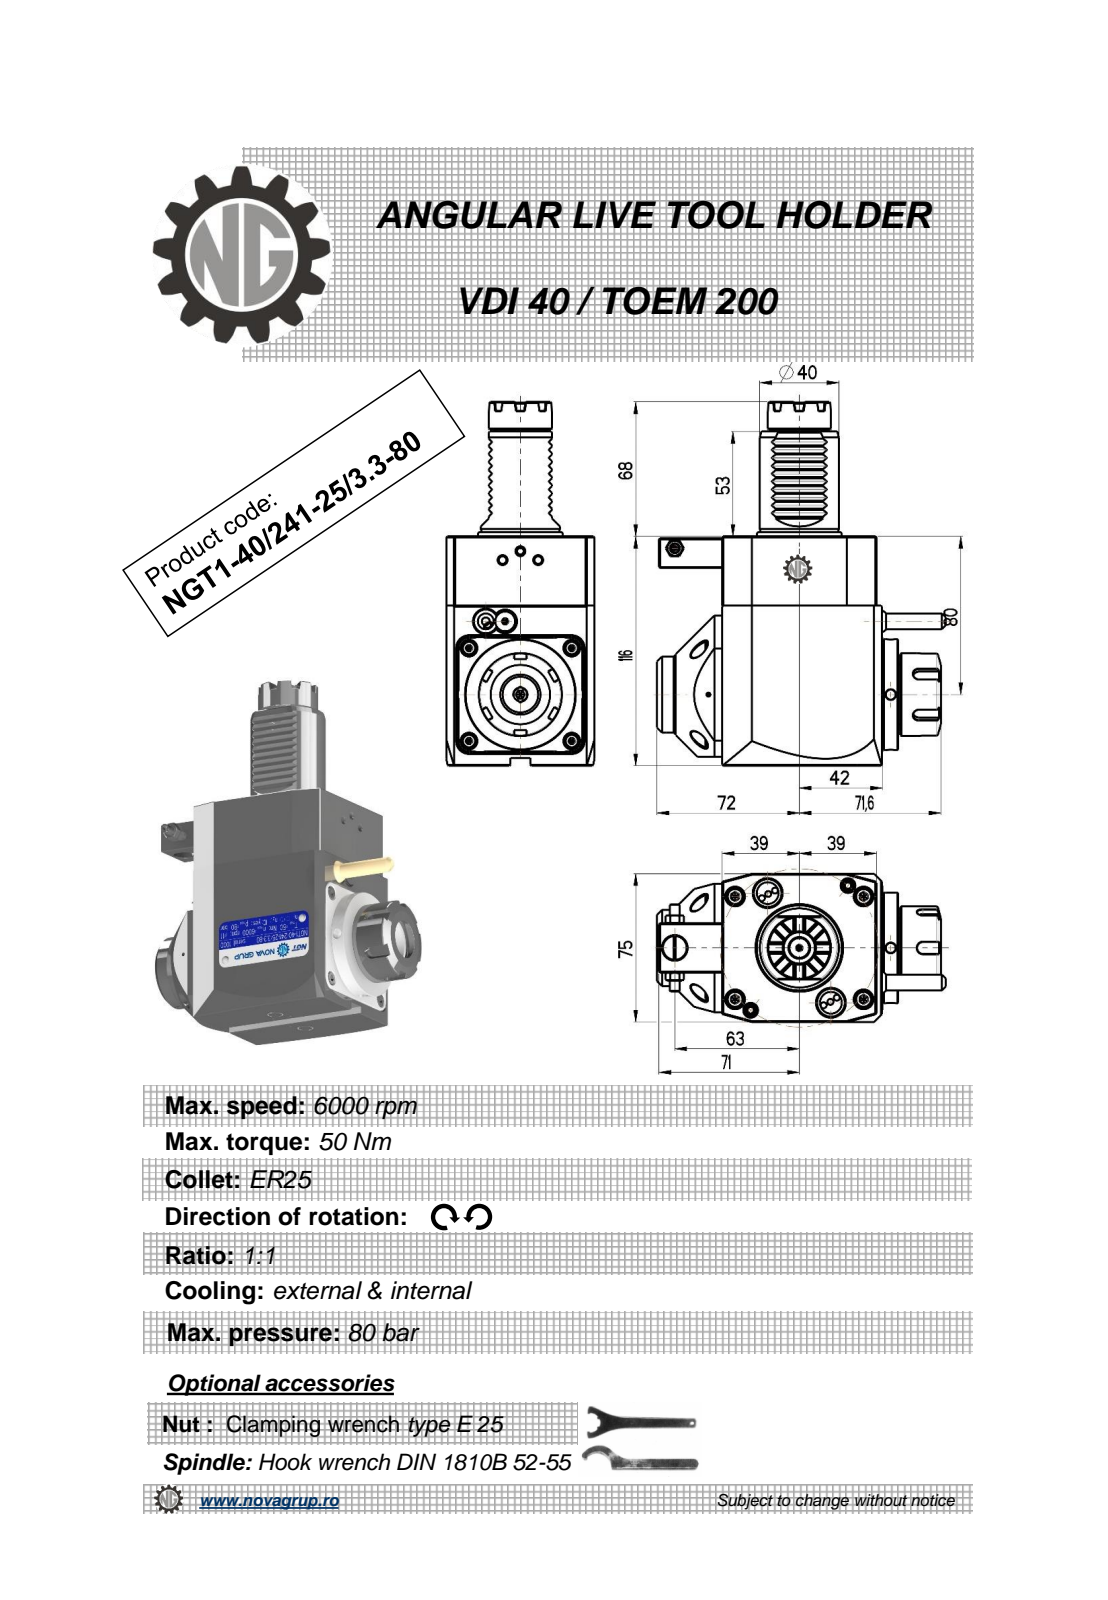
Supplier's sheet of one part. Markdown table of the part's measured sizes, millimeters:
| quantity | value |
| --- | --- |
| part name | NGT1_40_241_25_3_3_80 |
| STEP written by | PRO/ENGINEER BY PARAMETRIC TECHNOLOGY CORPORATION, 2010280 (CONFIG_CONTROL_DESIGN) |
| units | millimeters |
| bodies | 1 solid, 551 faces (263 planar, 96 cylindrical, 192 other) |
| overall size | 184 × 146.14 × 75 |
| volume | 889 418 mm³ |
| surface area | 73 235 mm² |
| round holes (diameter × count) | 5 × 3, 3 × 1, 4.2 × 1, 9.5 × 1, 12 × 1, 20.3 × 1 |
| round bosses / shafts (diameter × count) | 56 × 1, 43 × 1, 42 × 1, 40 × 1, 38.5 × 1, 33 × 1, 32 × 1, 17.2 × 1 |
| partial cylindrical surfaces (radius × count) | 0.3 × 20, 0.26 × 12, 0.2 × 6, 3 × 5, 40 × 1 |
| main face-to-face distances | 75, 116, 78, 81, 3, 11, 89, 8, 111, 80.8 |
| hole center spacings | 39.58, 40.93, 72.5, 109.25, 131.95 |
